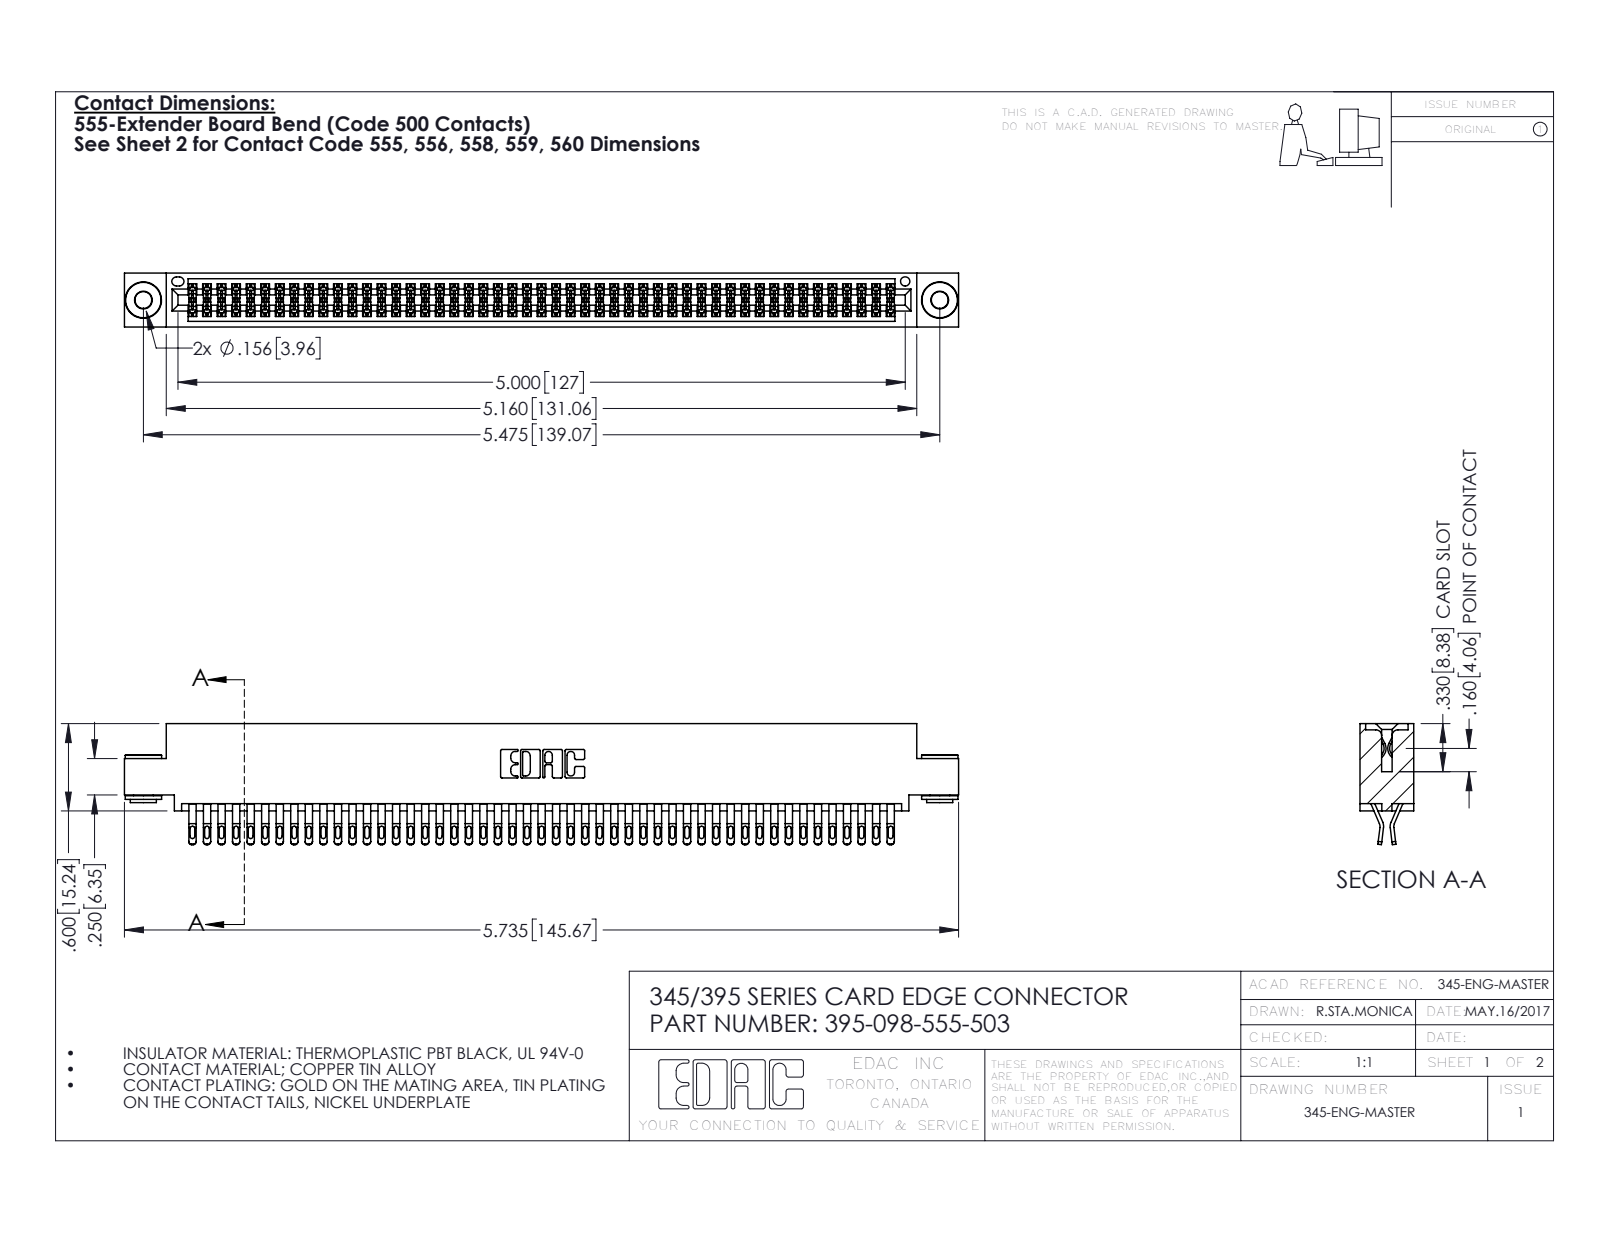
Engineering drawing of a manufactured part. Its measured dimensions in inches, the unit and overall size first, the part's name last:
Units: inches
Overall size (bounding box): 5.735 × 0.832 × 0.37
Round holes (diameter × count): ⌀0.116 ×2, ⌀0.156 ×2, ⌀0.064 ×1
Round bosses / shafts (diameter × count): ⌀0.25 ×2, ⌀0.18 ×2, ⌀0.136 ×2
Partial cylindrical surfaces — rounded edges, fillets, slot ends (radius × count): R0.016 ×245, R0.02 ×196, R0.006 ×147, R0.01 ×22, R0.007 ×6, R0.031 ×6, R0.026 ×3, R0.01 ×2
Main face-to-face distances: 0.072, 0.298, 0.025, 0.37, 0.2, 0.098, 0.272, 0.225, 0.175, 0.149
Hole centre spacings: 0.27, 5.239, 5.475
Volume: 0.882 in³ · Surface area: 35.3 in²
Bodies: 101 solids, 5656 faces (3132 planar, 2516 cylindrical, 8 other)
Part name (STEP PRODUCT): 345-250-002_345-250-002-102; 345 Part_0.110 Offset - 0.156 Dia-TH; 345-292-001_555 Tail; 395-098-555-503
STEP written by: SolidWorks 2016 (CONFIG_CONTROL_DESIGN)
